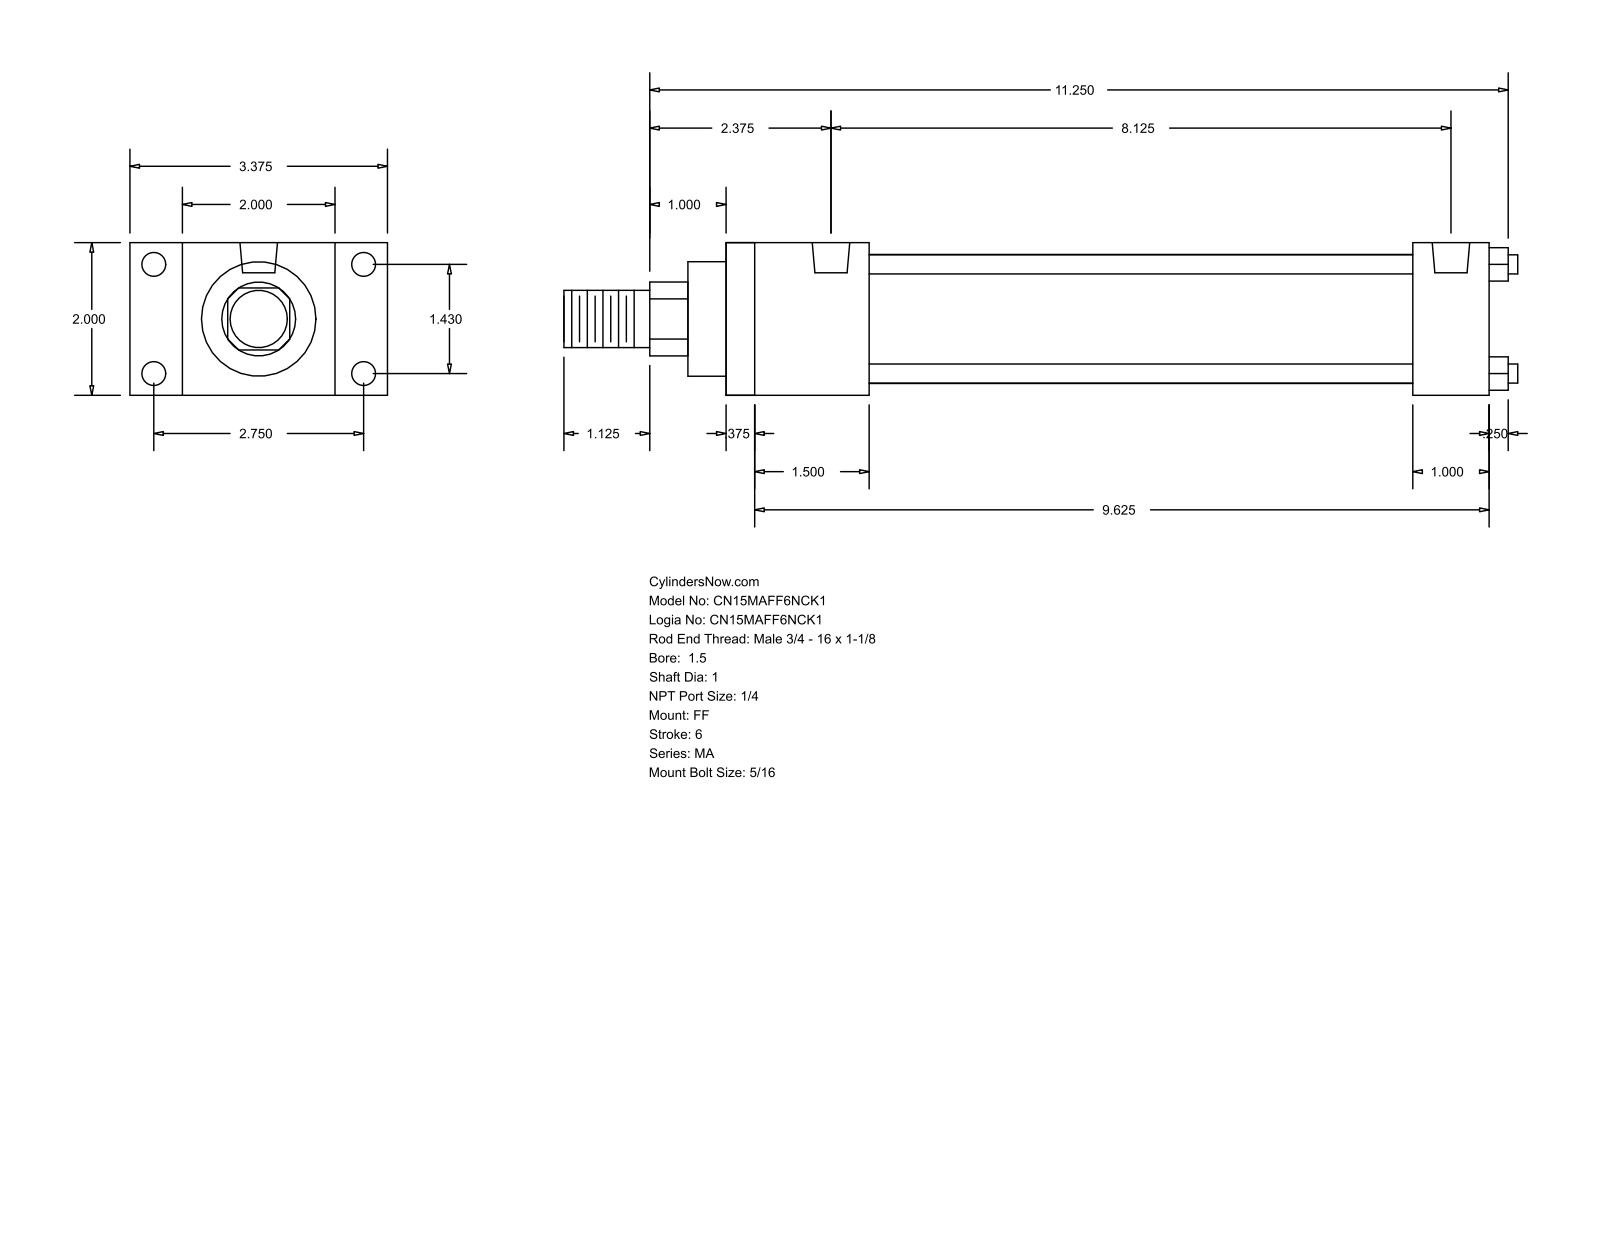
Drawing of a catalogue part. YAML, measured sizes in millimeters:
part_name: "MA_FF__0150_1"
step_written_by: "GSSL Pune (CONFIG_CONTROL_DESIGN)"
units: millimeters
bodies: {solids: 0, faces: 92, planar: 64, cylindrical: 28, other: 0}
overall_size: [317.5, 85.72, 50.8]
round_holes:
  - {diameter: 7.94, count: 8}
  - {diameter: 12.49, count: 2}
round_bosses_or_shafts:
  - {diameter: 6.35, count: 4}
  - {diameter: 42.93, count: 1}
  - {diameter: 38.1, count: 1}
  - {diameter: 25.4, count: 1}
  - {diameter: 19.05, count: 1}
partial_cylinders:
  - {radius: 12.29, count: 1}
face_to_face_distances: [50.8, 254, 9.52, 244.48, 25.4, 47.63, 228.6, 38.11, 219.08, 180.97]
hole_center_spacings: [36.32, 69.84, 78.72, 206.37]
